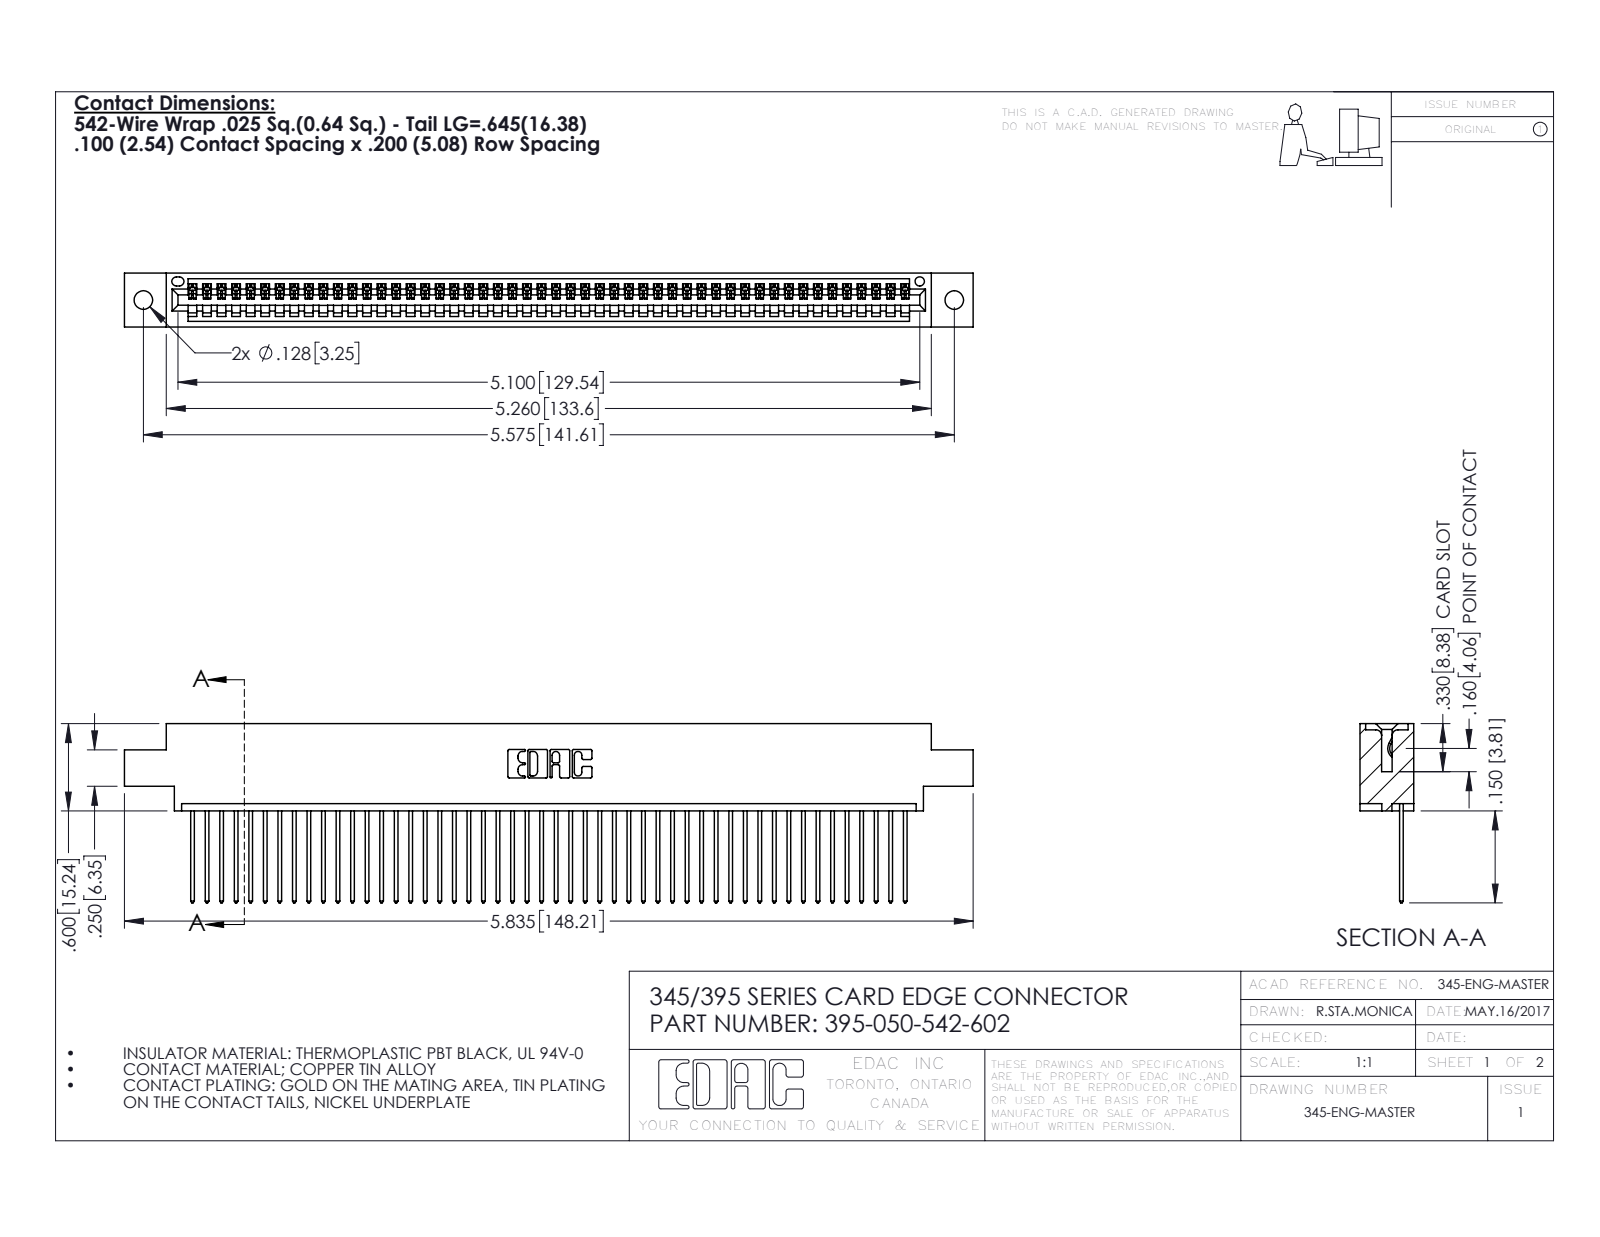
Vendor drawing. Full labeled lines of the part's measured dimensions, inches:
Part name (STEP PRODUCT): 345-292-001_345-293-142; 395-050-542-602; 345 Part_0.170 Offset - 0.128 Dia
STEP written by: SolidWorks 2016 (CONFIG_CONTROL_DESIGN)
Units: inches
Bodies: 51 solids, 3030 faces (2084 planar, 946 cylindrical, 0 other)
Overall size (bounding box): 5.835 × 1.232 × 0.37
Volume: 0.861 in³ · Surface area: 30.09 in²
Round holes (diameter × count): ⌀0.128 ×2, ⌀0.064 ×1
Partial cylindrical surfaces — rounded edges, fillets, slot ends (radius × count): R0.006 ×100, R0.01 ×100, R0.01 ×22, R0.007 ×6, R0.031 ×6, R0.026 ×3, R0.031 ×2, R0.04 ×2
Main face-to-face distances: 0.072, 0.298, 0.37, 0.098, 0.272, 0.025, 0.2, 0.225, 0.175, 0.149
Hole centre spacings: 0.27, 5.339, 5.575
